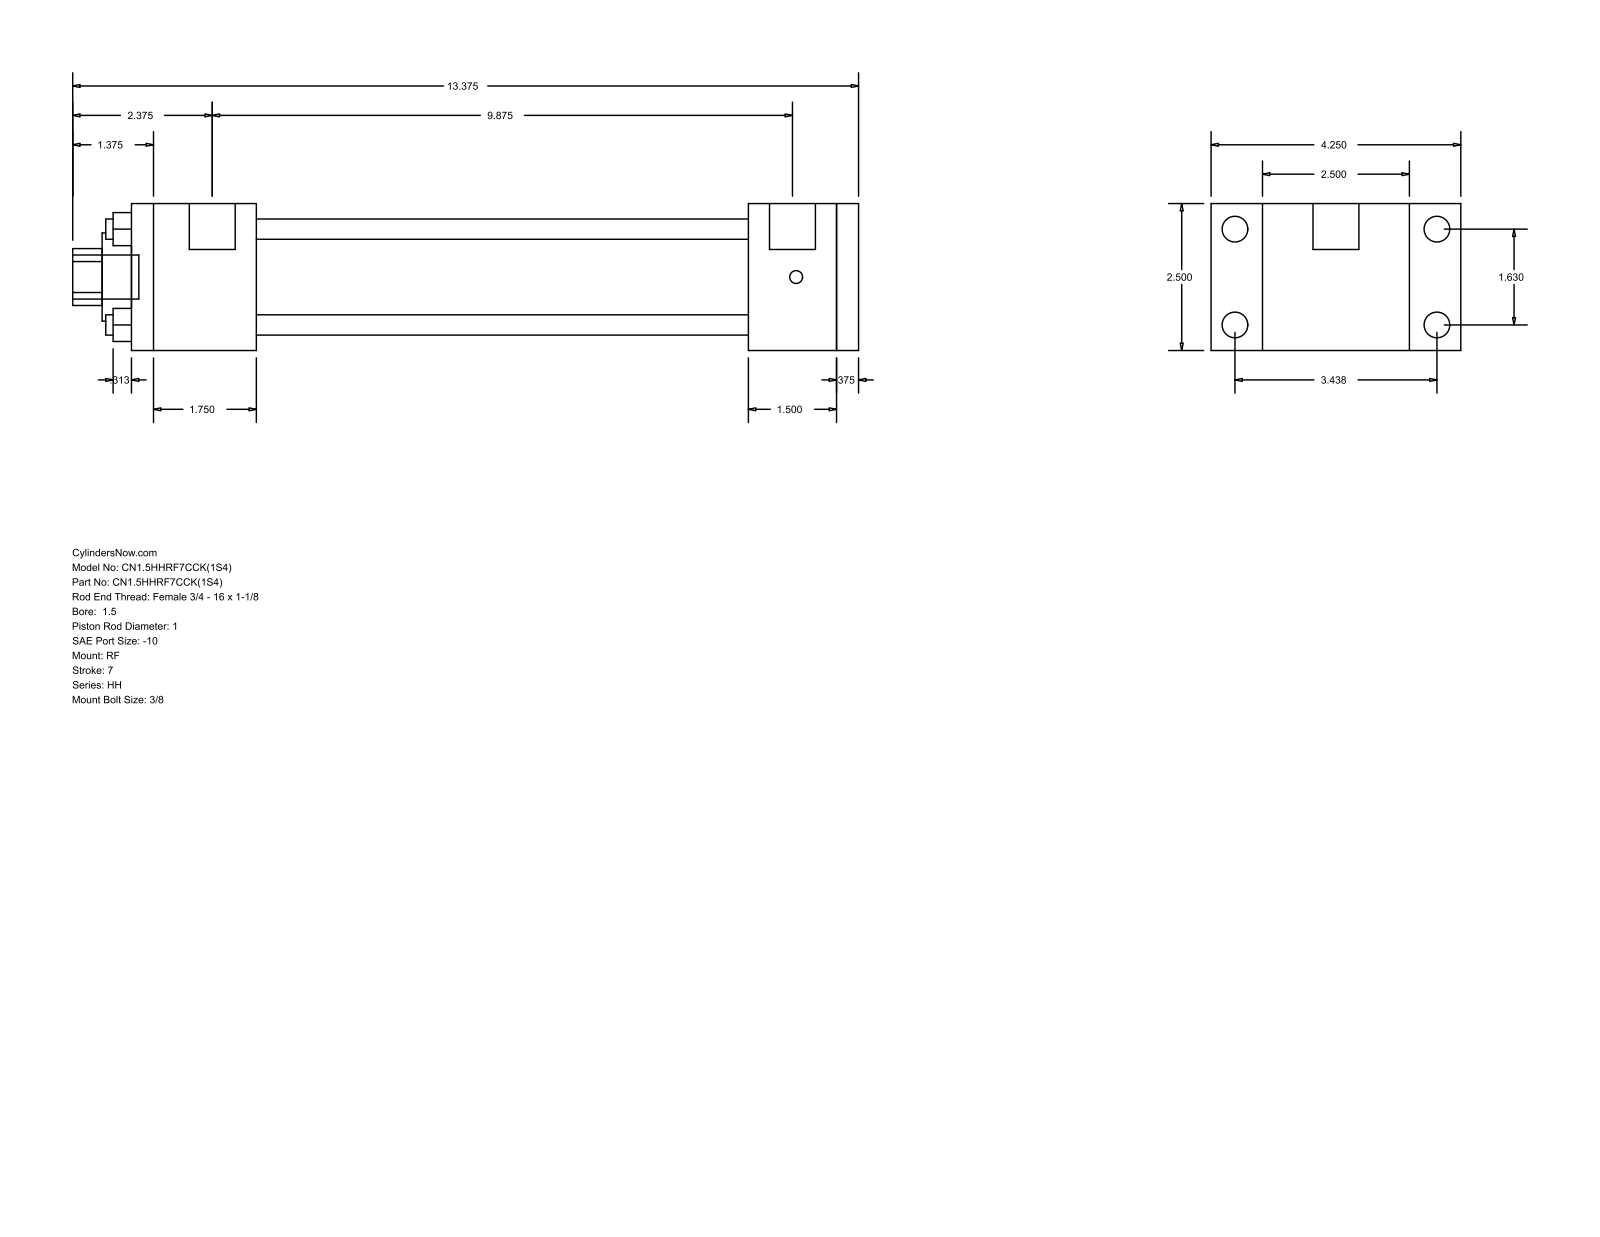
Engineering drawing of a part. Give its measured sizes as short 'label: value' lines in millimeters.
name: HH_RF__0150_1
written by: GSSL Pune (CONFIG_CONTROL_DESIGN)
unit: mm
bodies: 0 solids, 92 faces (64 planar, 28 cylindrical, 0 other)
size: 339.73 × 107.95 × 63.5
holes: 4× ⌀8.76, 1× ⌀25.4, 1× ⌀38.1, 1× ⌀44.45
bosses: 4× ⌀11.13, 4× ⌀5.56, 2× ⌀19.84, 1× ⌀19.05
rounds: 1× R12.29
face distances: 63.5, 9.53, 212.72, 250.82, 260.35, 38.1, 47.63, 53.98, 266.7, 304.8
hole spacings: 29.27, 41.4, 58.55
